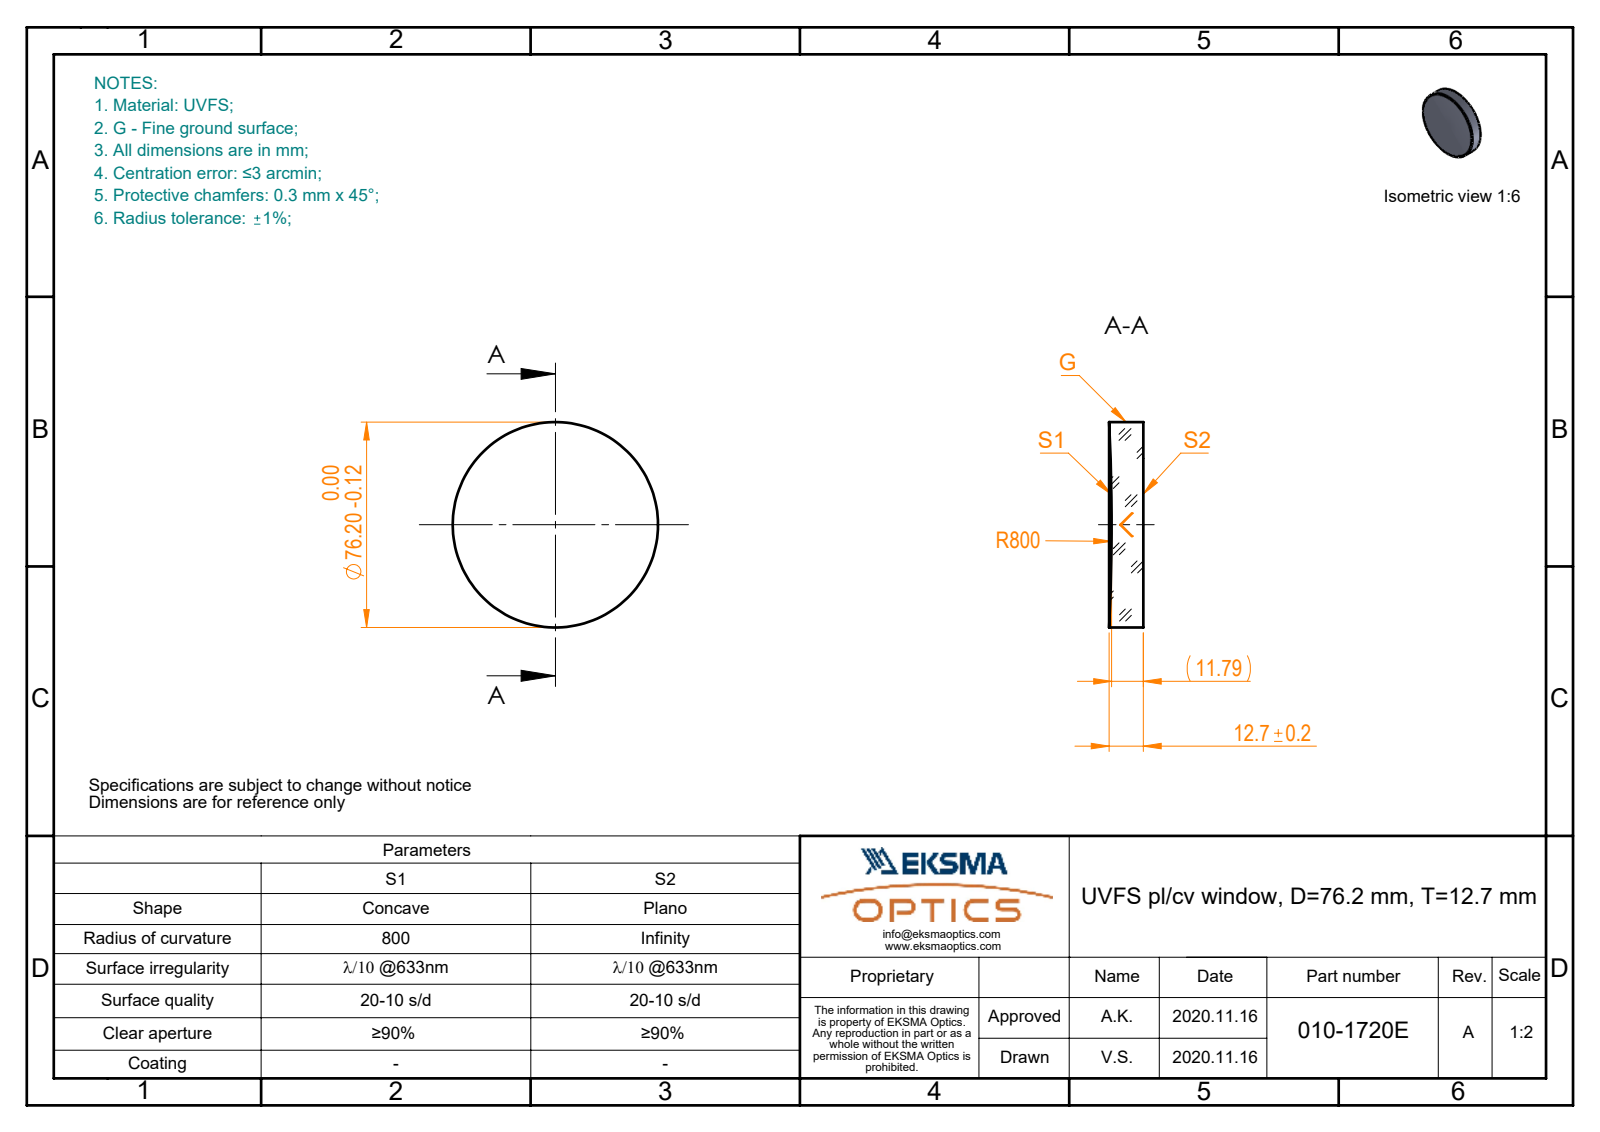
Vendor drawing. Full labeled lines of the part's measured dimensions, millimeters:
Part name (STEP PRODUCT): 010-1720E_UVFS_PCV_window
STEP written by: SolidWorks 2019 (CONFIG_CONTROL_DESIGN)
Units: millimetres
Bodies: 1 solid, 5 faces (1 planar, 2 cylindrical, 2 other)
Overall size (bounding box): 76.2 × 76.2 × 12.7
Volume: 55 846 mm³ · Surface area: 12 164 mm²
Round bosses / shafts (diameter × count): ⌀76.2 ×1
